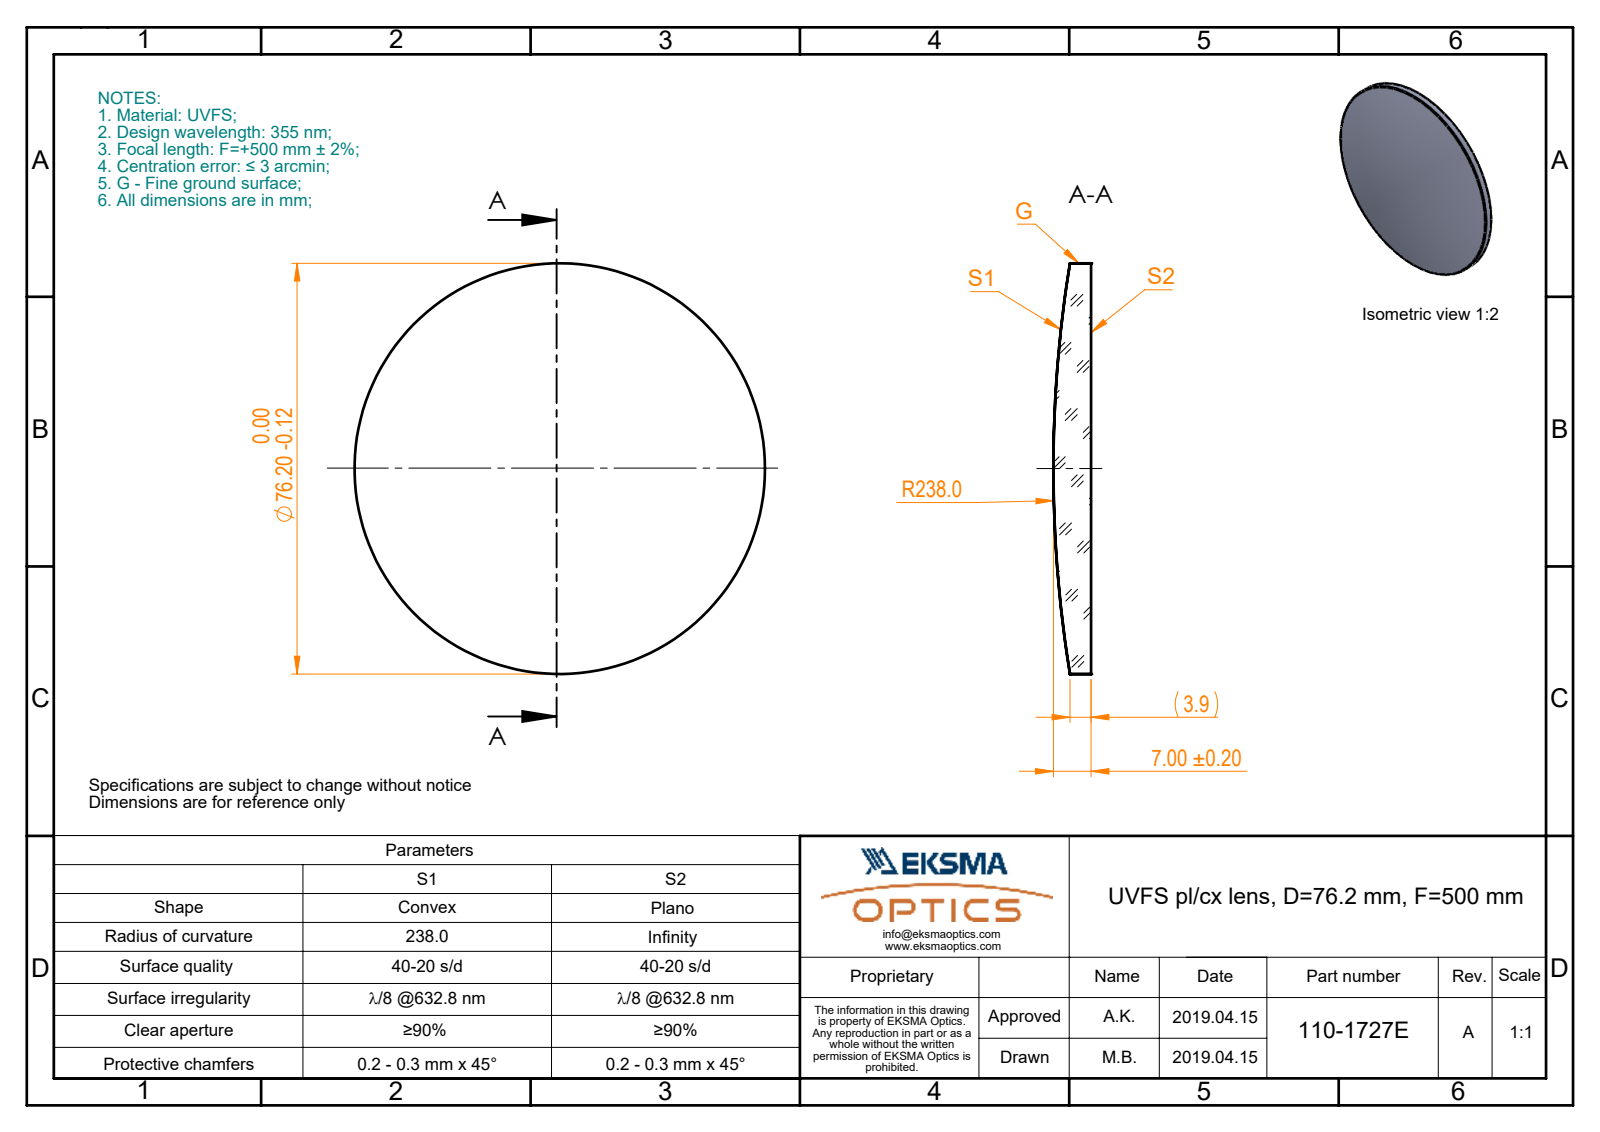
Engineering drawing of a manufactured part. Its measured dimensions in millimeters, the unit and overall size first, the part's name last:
Units: millimetres
Overall size (bounding box): 76.2 × 76.2 × 7
Round bosses / shafts (diameter × count): ⌀76.2 ×1
Volume: 24 939 mm³ · Surface area: 10 091 mm²
Bodies: 1 solid, 5 faces (1 planar, 2 cylindrical, 2 other)
Part name (STEP PRODUCT): 110-1727E UVFS pl-cx 76.2 F500
STEP written by: SolidWorks 2017 (CONFIG_CONTROL_DESIGN)
